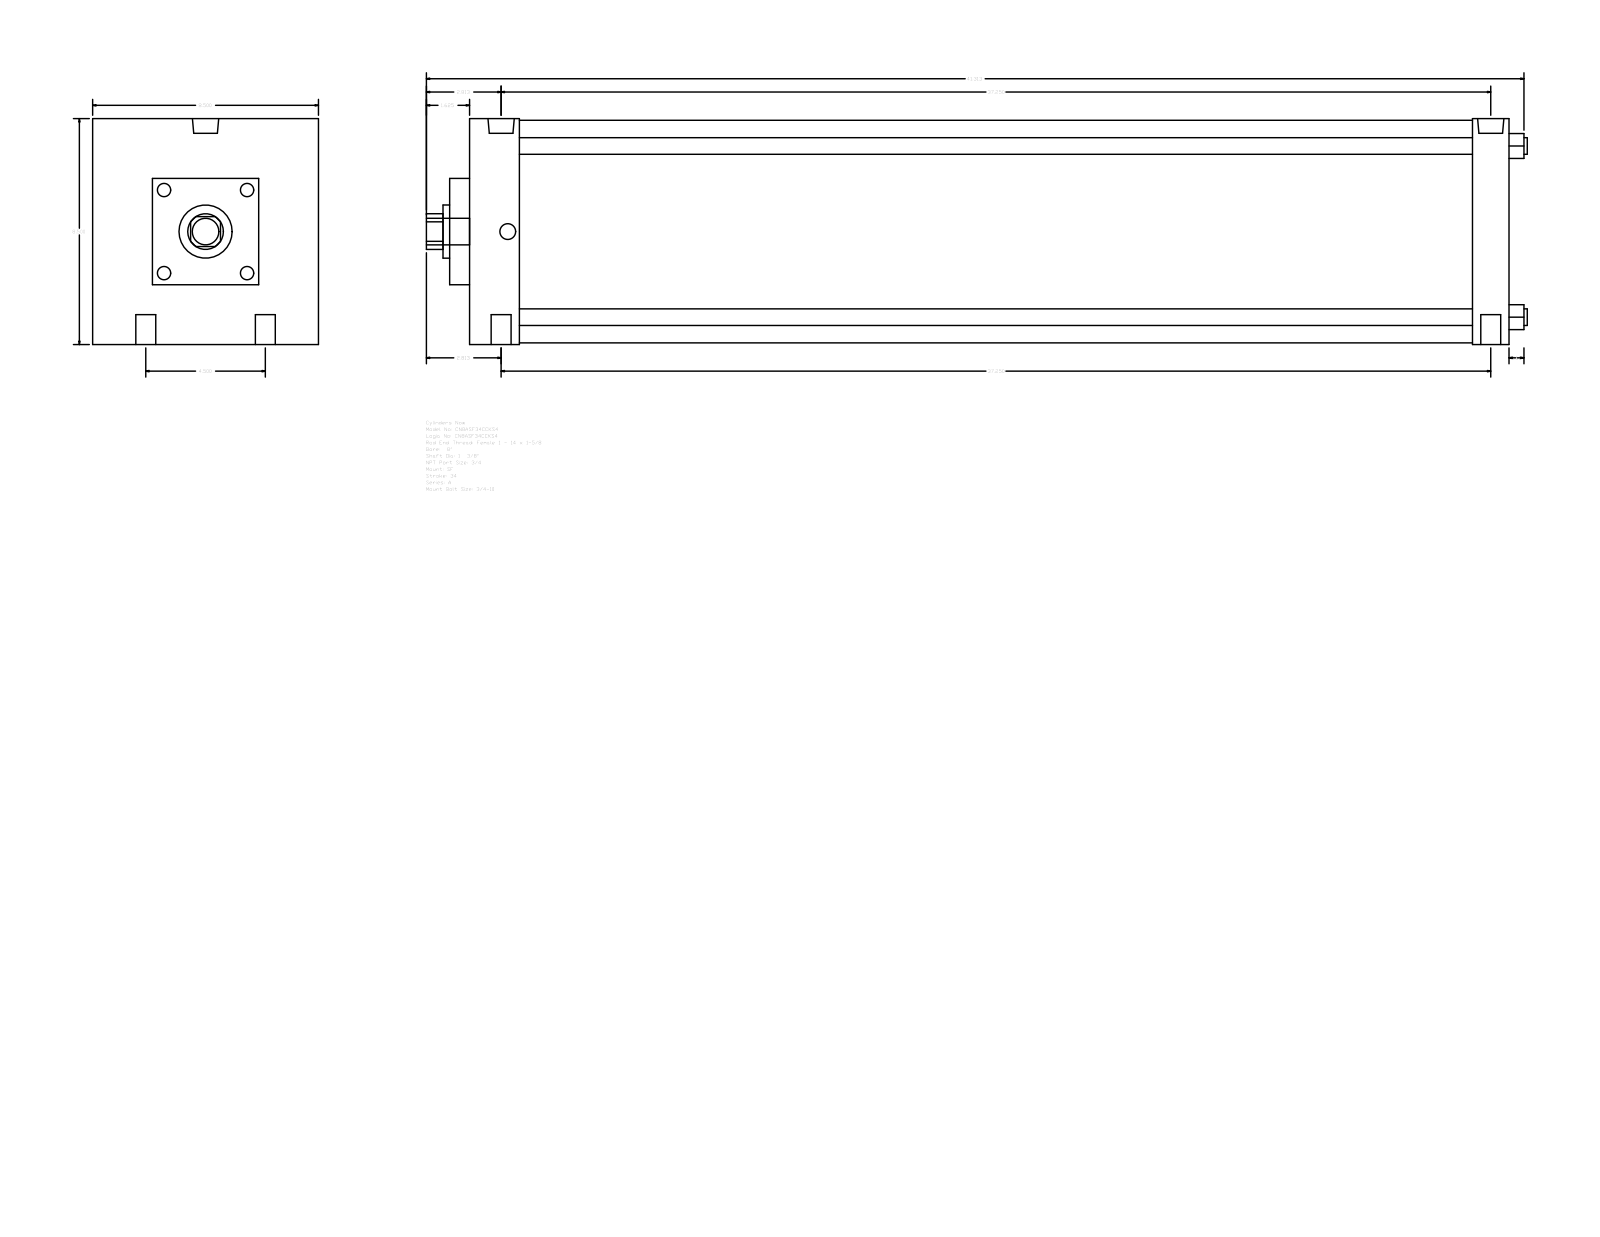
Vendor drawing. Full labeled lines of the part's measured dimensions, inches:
Part name (STEP PRODUCT): A_SF__0800_1.375
STEP written by: GSSL Pune (CONFIG_CONTROL_DESIGN)
Units: inches
Bodies: 0 solids, 93 faces (67 planar, 26 cylindrical, 0 other)
Overall size (bounding box): 41.437 × 8.5 × 8.5
Round holes (diameter × count): ⌀0.75 ×4, ⌀0.594 ×2, ⌀0.989 ×2, ⌀1.375 ×1, ⌀2 ×1
Round bosses / shafts (diameter × count): ⌀0.625 ×4, ⌀8.375 ×1, ⌀1 ×1
Partial cylindrical surfaces — rounded edges, fillets, slot ends (radius × count): R0.672 ×1
Main face-to-face distances: 39.125, 8.5, 1.875, 37.75, 35.875, 37.25, 1.375, 0.75, 2.625, 38.5
Hole centre spacings: 2.25, 37.318, 37.25, 4.5, 37.521, 36.75
